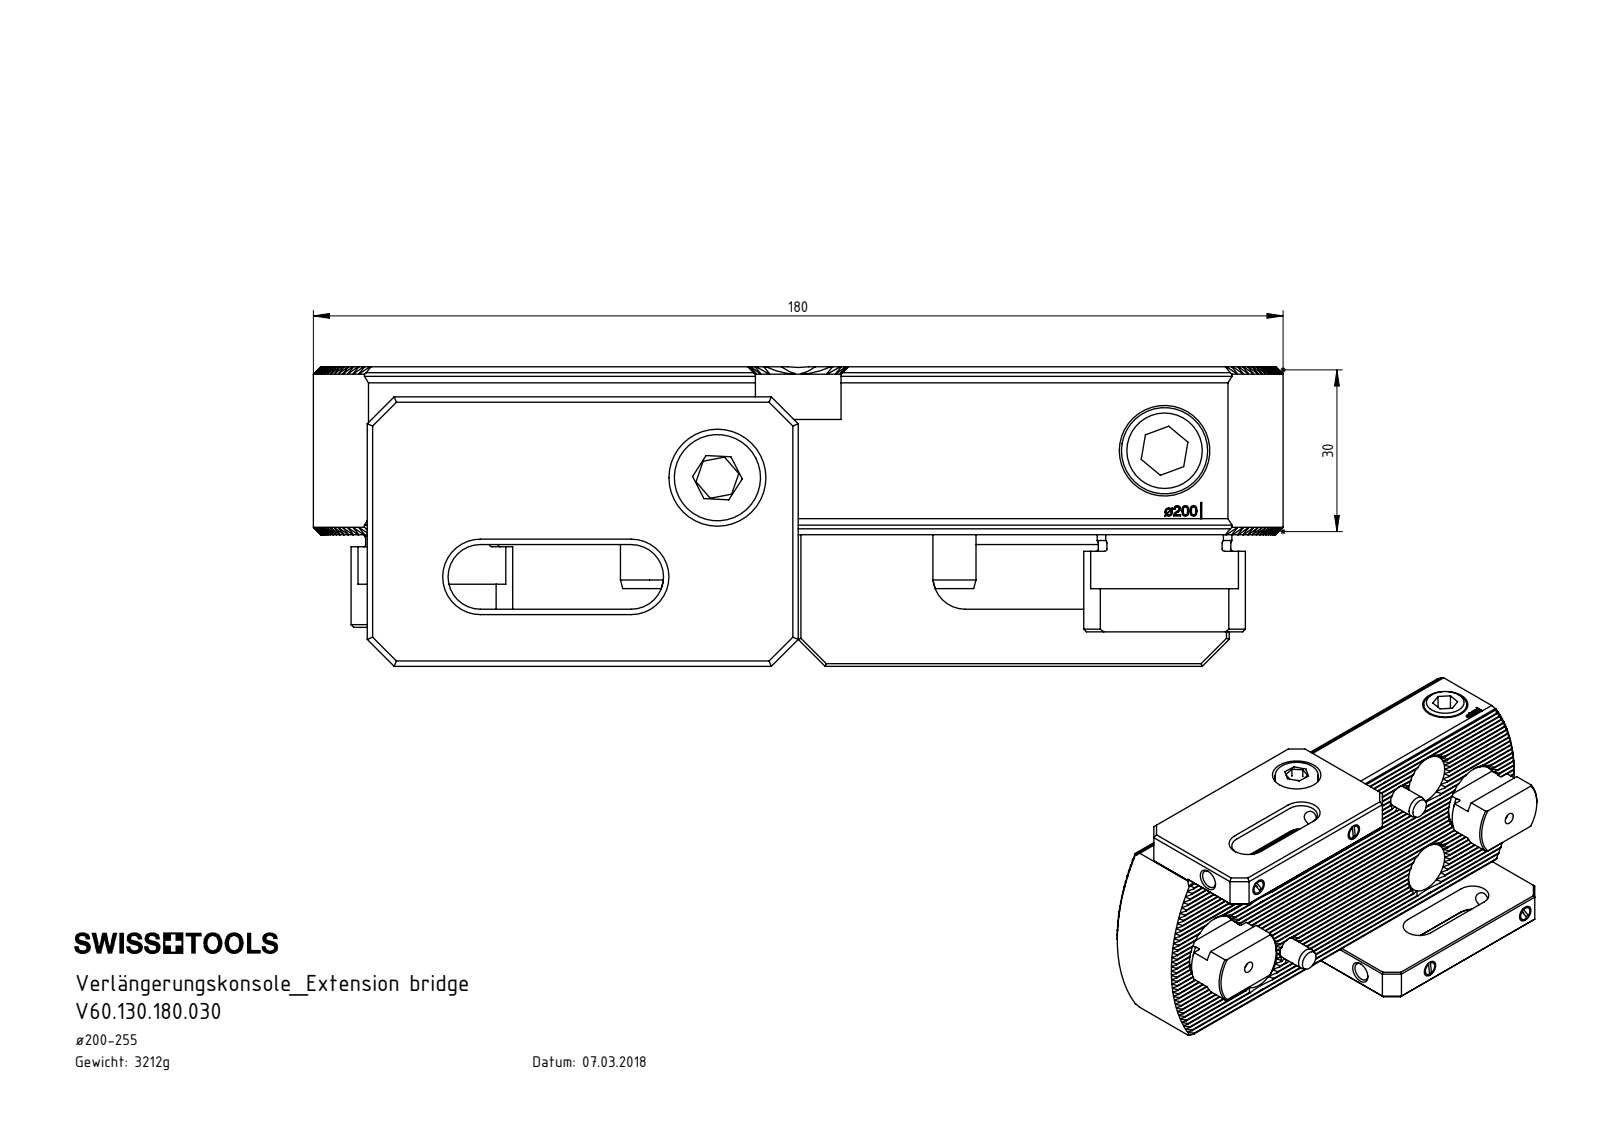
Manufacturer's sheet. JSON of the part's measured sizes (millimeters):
{"part_name": "Ko1.VK1.180.030; VK1-ER7.001.012; VK1-ER3.001.028_A; VK1-ER2.201.010_A_vorgespannt (+8 more)", "step_written_by": "SolidWorks 2017 (AUTOMOTIVE_DESIGN)", "units": "millimeters", "bodies": {"solids": 25, "faces": 1483, "planar": 971, "cylindrical": 299, "other": 213}, "overall_size": [180, 95, 55.58], "volume_mm3": 418743, "surface_area_mm2": 114295, "round_holes": [[5, 4], [6, 4], [6.8, 4], [13, 4], [19, 4], [2, 2], [8, 2], [8.5, 2], [10.5, 2], [11, 2], [14, 2], [18, 2]], "round_bosses_or_shafts": [[16, 4], [6, 4], [10, 2]], "partial_cylinders_radius": [[0.14, 66], [2, 8], [6, 4], [12.3, 2], [15, 2], [65, 2], [7.95, 1]], "face_to_face_distances": [12, 82, 70, 1.73, 0.5, 82.5, 11.5, 70.5, 94, 3.46], "hole_center_spacings": [31.24, 113.77, 136, 7.9, 15, 18.55, 19.61, 31.89]}
